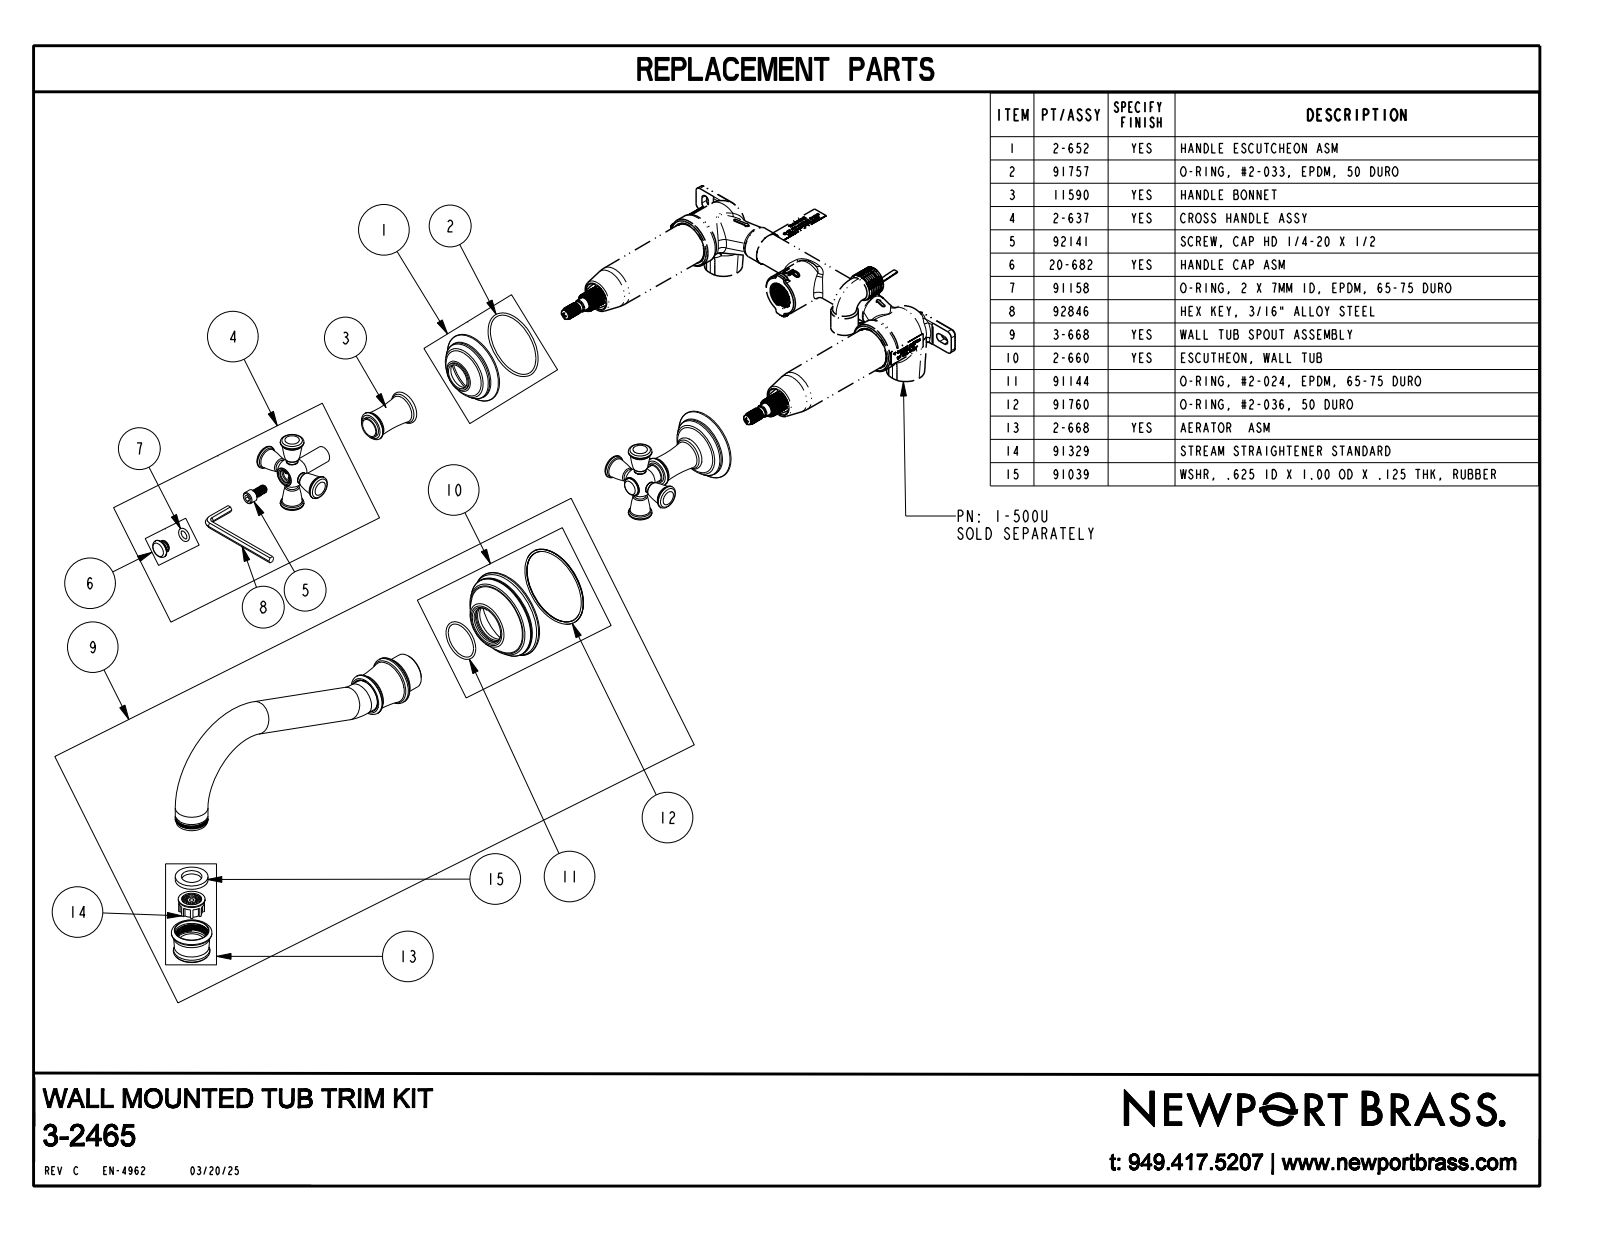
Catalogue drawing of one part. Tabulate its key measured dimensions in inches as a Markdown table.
| quantity | value |
| --- | --- |
| part name | 3-2465_SW0001 |
| STEP written by | CREO PARAMETRIC BY PTC INC, 2018400 (AUTOMOTIVE_DESIGN) |
| units | inches |
| bodies | 3 solids, 333 faces (21 planar, 60 cylindrical, 252 other) |
| overall size | 10.403 × 10.323 × 8.808 |
| volume | 20.56 in³ |
| surface area | 99.13 in² |
| round bosses / shafts (diameter × count) | 1 × 3, 0.72 × 3, 0.36 × 3, 0.9 × 2, 0.649 × 2, 0.56 × 2, 0.517 × 2, 1.5 × 1 |
| main face-to-face distances | 2.14, 2.2, 0.06, 2.22, 0.08, 0.02, 1.004, 1.136, 1.196, 1.216 |
